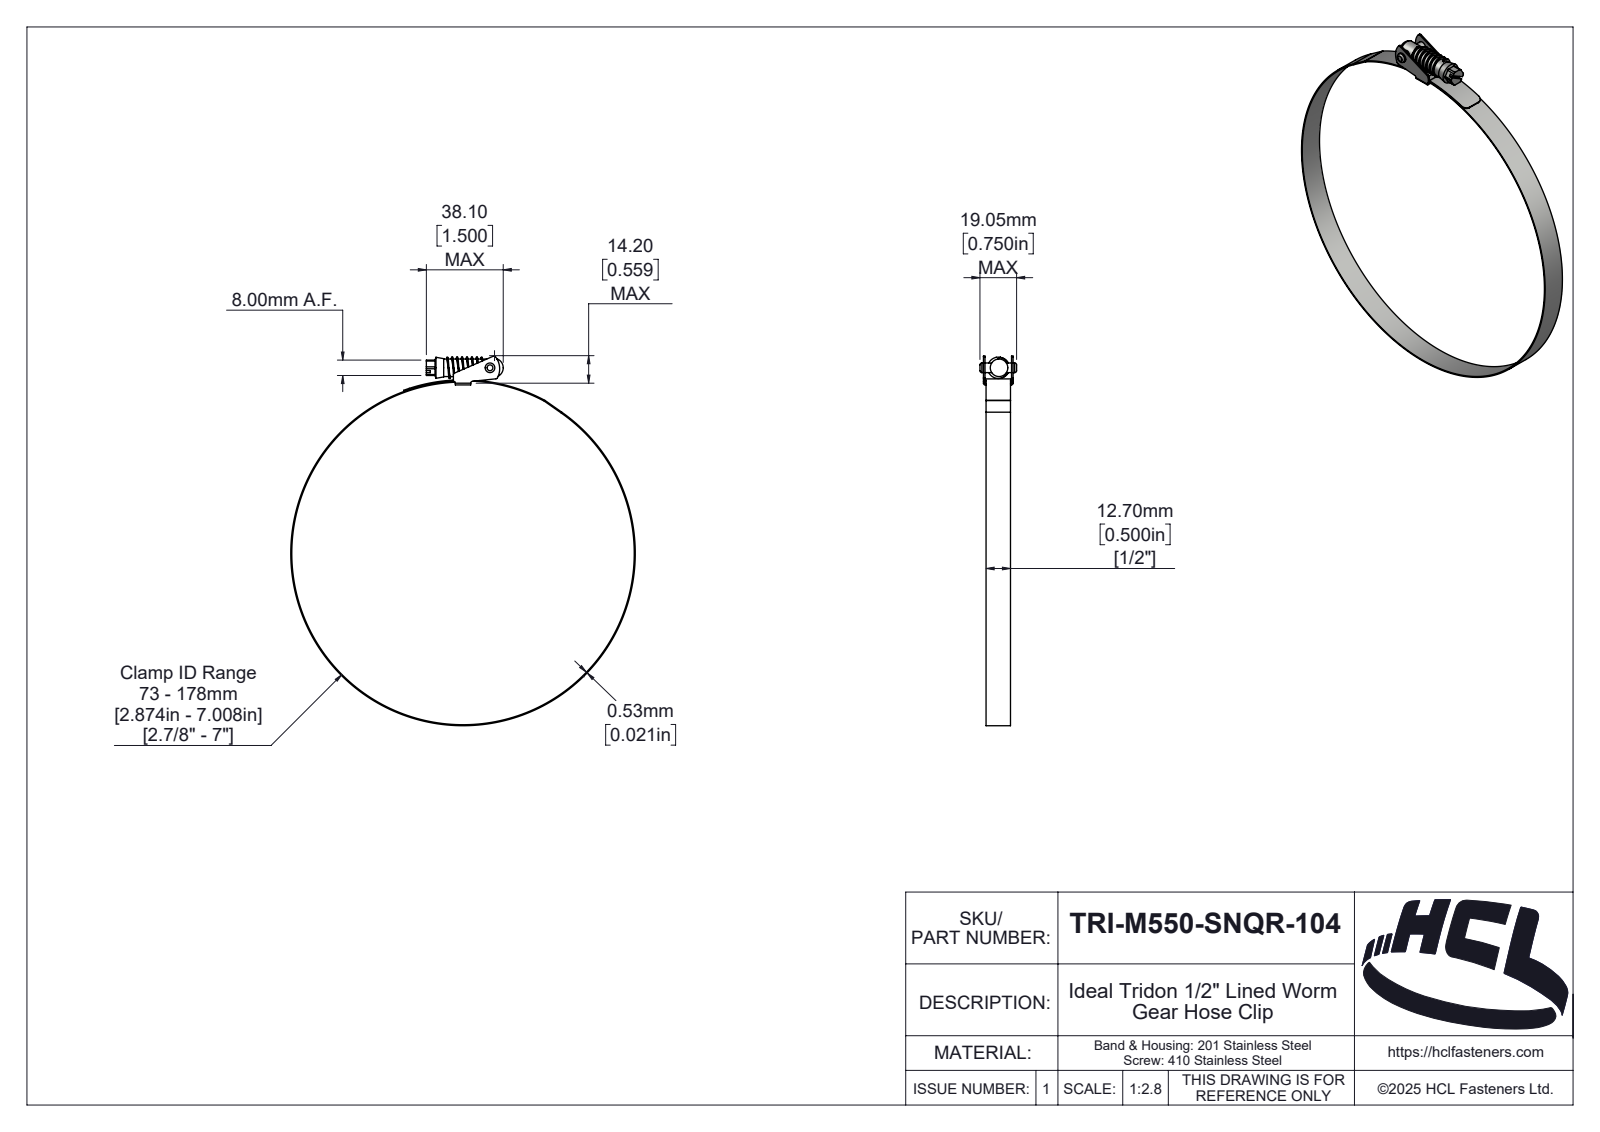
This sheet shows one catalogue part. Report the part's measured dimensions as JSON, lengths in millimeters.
{"part_name": "TRI-M550-SNQR-104", "step_written_by": "SolidWorks 2025 (AUTOMOTIVE_DESIGN)", "units": "millimeters", "bodies": {"solids": 5, "faces": 222, "planar": 44, "cylindrical": 112, "other": 66}, "overall_size": [192.02, 179.06, 19.05], "volume_mm3": 7167, "surface_area_mm2": 19262, "round_holes": [[5, 1], [178, 1]], "round_bosses_or_shafts": [[179.06, 1], [9.1, 1]], "partial_cylinders_radius": [[1, 11], [0.1, 2], [0.9, 2], [3, 2], [0.46, 1], [1.89, 1], [2, 1], [2.35, 1]], "face_to_face_distances": [0.8, 1.35, 14.05, 14.6, 0.55, 13.25, 12.7, 15.4, 13.8, 0.53], "hole_center_spacings": [97.41]}
